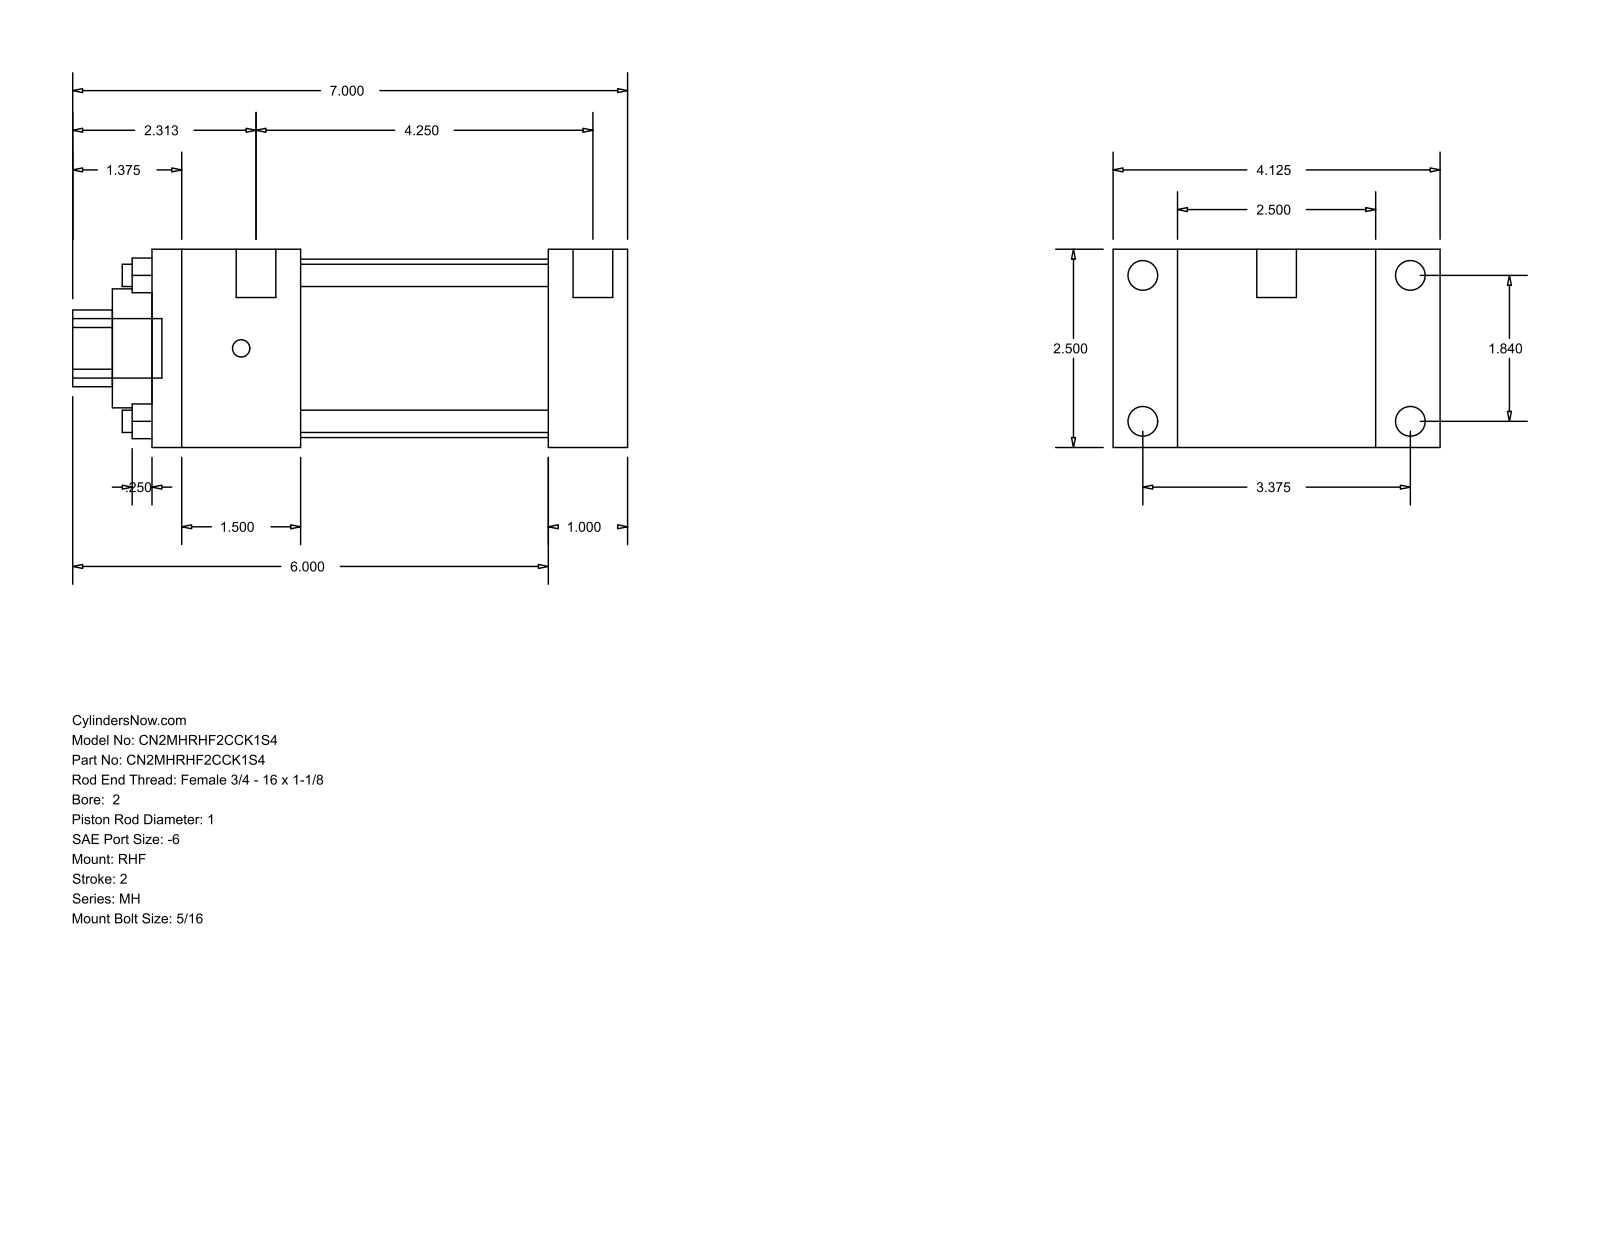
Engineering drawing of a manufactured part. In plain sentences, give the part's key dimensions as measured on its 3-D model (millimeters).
The part is named "MH_RHF__0200_1". Its 3-D file was written by "GSSL Pune (CONFIG_CONTROL_DESIGN)". It is 0 solids with 88 faces: 60 planar, 28 cylindrical and 0 other. Overall it measures 177.8 by 104.78 by 63.5 millimeters. Round holes: 4 of diameter 7.14, 1 of diameter 25.4, 1 of diameter 38.1, 1 of diameter 57.15. Round bosses or shafts: 4 of diameter 9.53, 4 of diameter 5.56, 2 of diameter 12.7, 1 of diameter 19.05. Partial cylindrical surfaces (rounded edges, fillets, slot ends): 1 of radius 12.29. The main face-to-face distances are 63.5, 25.4, 20.64, 84.14, 152.4, 127, 104.78, 104.77, 47.63, 79.37. The hole center spacings are 33.05, 46.74, 66.1.
